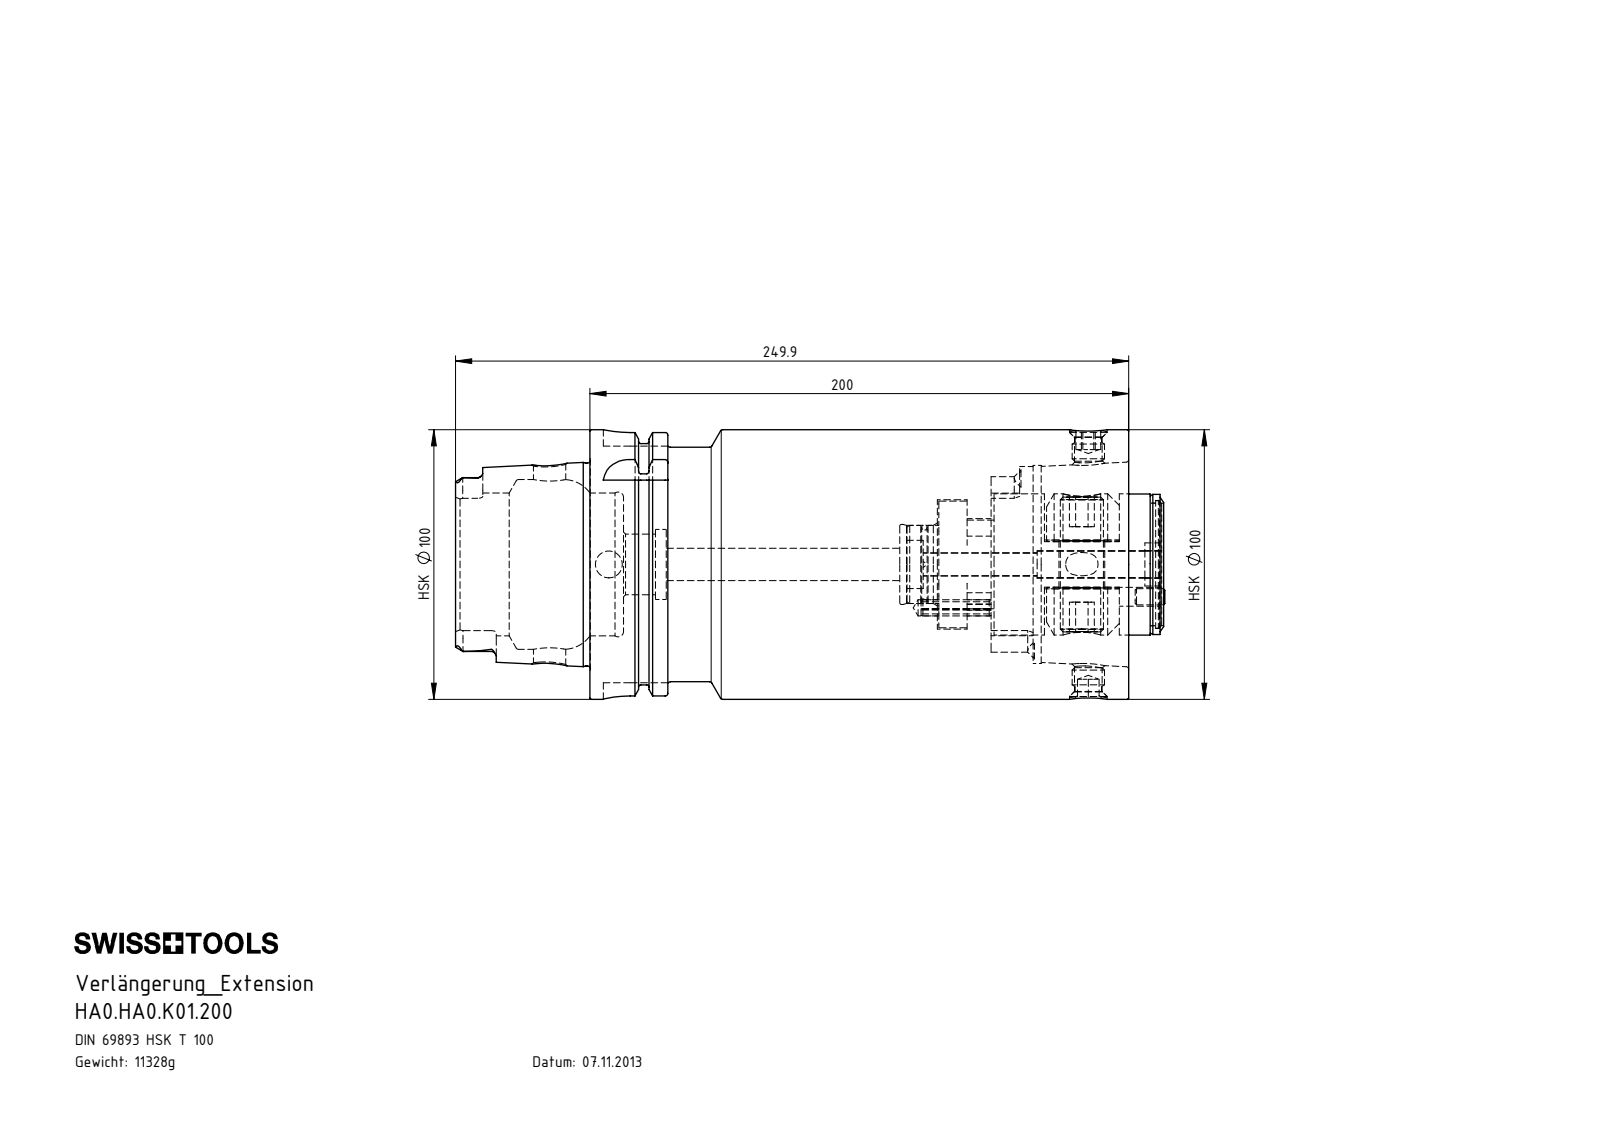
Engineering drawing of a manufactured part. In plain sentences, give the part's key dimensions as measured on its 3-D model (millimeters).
The part is named "HA0.HA0.K01.200; HA0-ER2.001.012; ISO 13337 - 6 x 26_Default; HA0-ER1.001.000 (+7 more)". Its 3-D file was written by "SolidWorks 2011 (AUTOMOTIVE_DESIGN)". It is 11 solids with 472 faces: 148 planar, 158 cylindrical and 166 other. Overall it measures 263.3 by 100 by 100 millimeters. Its volume is 1 442 000 cubic millimeters and its surface area 170 958 square millimeters. Round holes: 3 of diameter 10, 3 of diameter 14, 2 of diameter 8.5, 2 of diameter 12, 1 of diameter 4.5, 1 of diameter 6, 1 of diameter 7, 1 of diameter 10.25, 1 of diameter 17, 1 of diameter 17.9, 1 of diameter 22.5, 1 of diameter 26. Round bosses or shafts: 1 of diameter 100, 1 of diameter 91.95, 1 of diameter 87, 1 of diameter 75.26, 1 of diameter 52.4, 1 of diameter 52, 1 of diameter 47.3, 1 of diameter 32.9. Partial cylindrical surfaces (rounded edges, fillets, slot ends): 6 of radius 1.9, 6 of radius 4, 6 of radius 5, 4 of radius 4.85, 4 of radius 8, 4 of radius 10, 3 of radius 3, 2 of radius 4.83. The main face-to-face distances are 200, 148.9, 51.1, 196.5, 47.6, 3.5, 12.45, 136.45, 184.05, 187.55. The hole center spacings are 11, 16.28, 12, 13.68, 16.39, 20.82, 22, 28.99.
